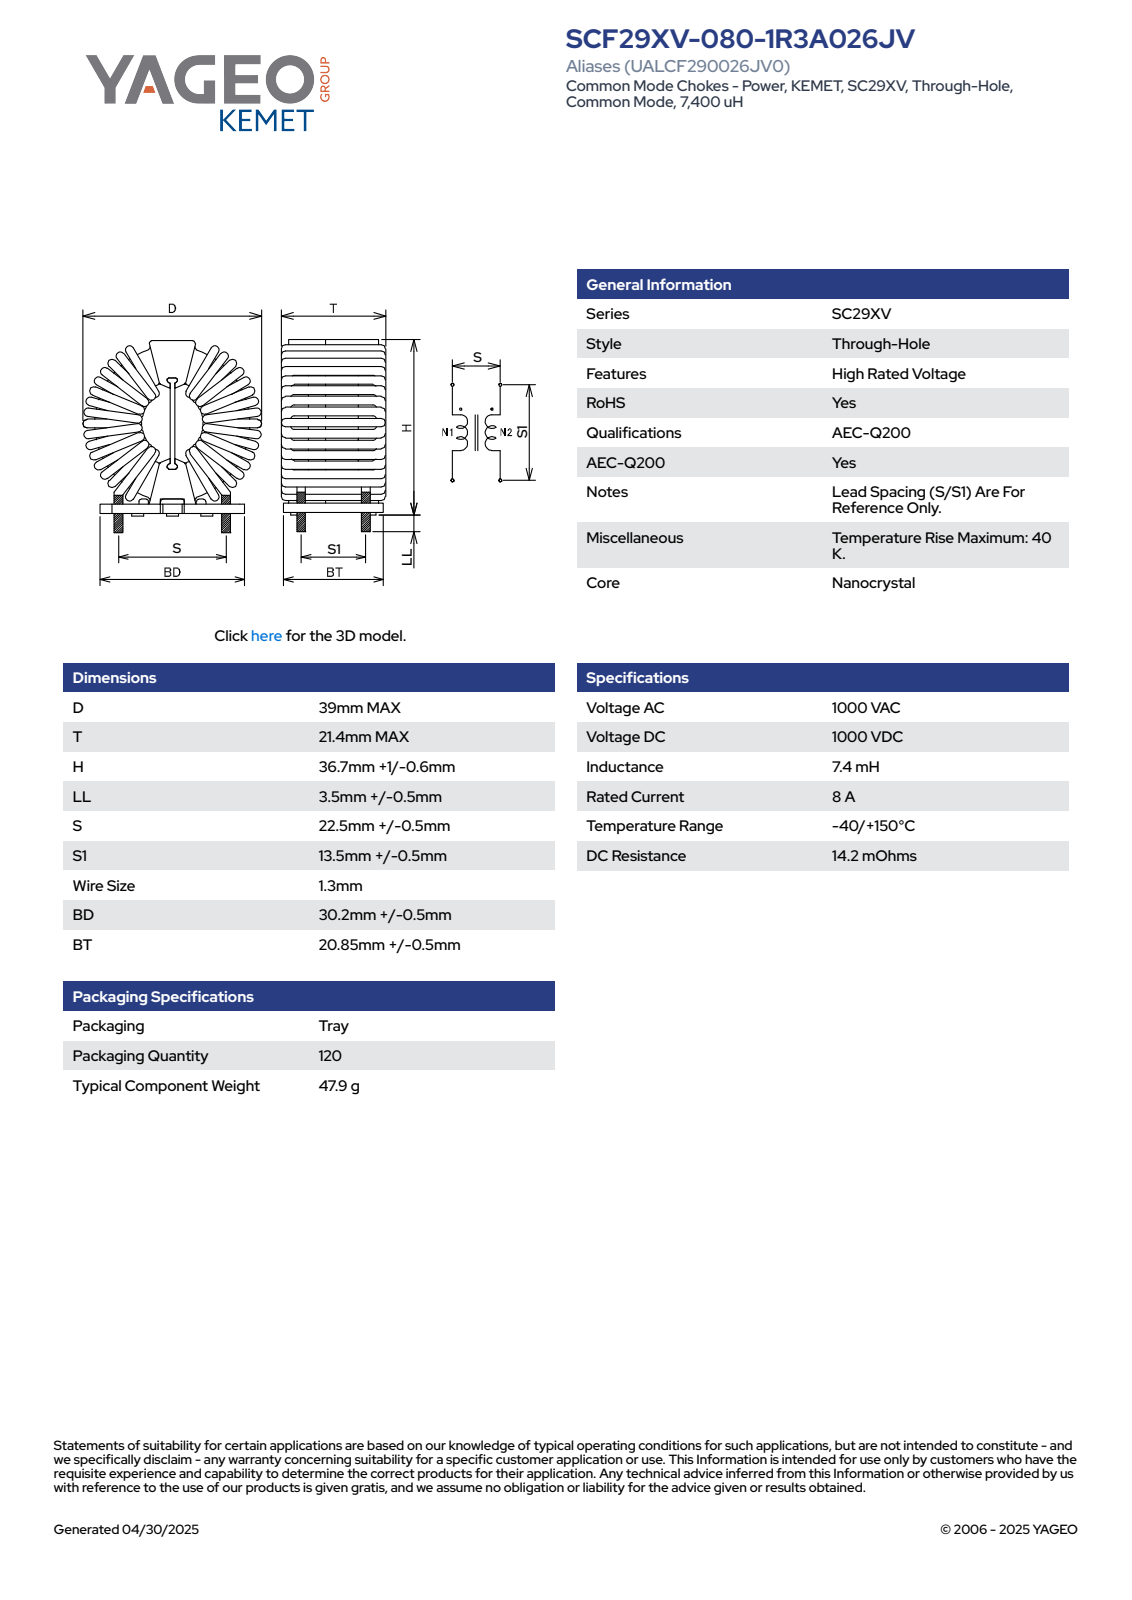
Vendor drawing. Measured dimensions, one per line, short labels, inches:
name: 簡易版_SC29XV-080-1R3A026JV
written by: SolidWorks 2022 (AUTOMOTIVE_DESIGN)
unit: in
bodies: 4 solids, 575 faces (281 planar, 197 cylindrical, 97 other)
size: 1.622 × 1.535 × 0.843
volume: 1.224 in³; area: 15.43 in²
holes: 4× ⌀0.067, 4× ⌀0.079, 4× ⌀0.118, 2× ⌀0.047, 2× ⌀0.055
bosses: 4× ⌀0.051, 3× ⌀0.098
rounds: 34× R0.02, 16× R0.012, 12× R0.051, 7× R0.039, 4× R0.03, 4× R0.059, 4× R0.132, 2× R0.776
face distances: 0.039, 0.843, 0.079, 0.205, 0.537, 0.742, 0.02, 0.059, 0.577, 0.165
hole spacings: 0.143, 0.633, 0.783, 0.997, 0.041, 0.259, 0.262, 0.295
